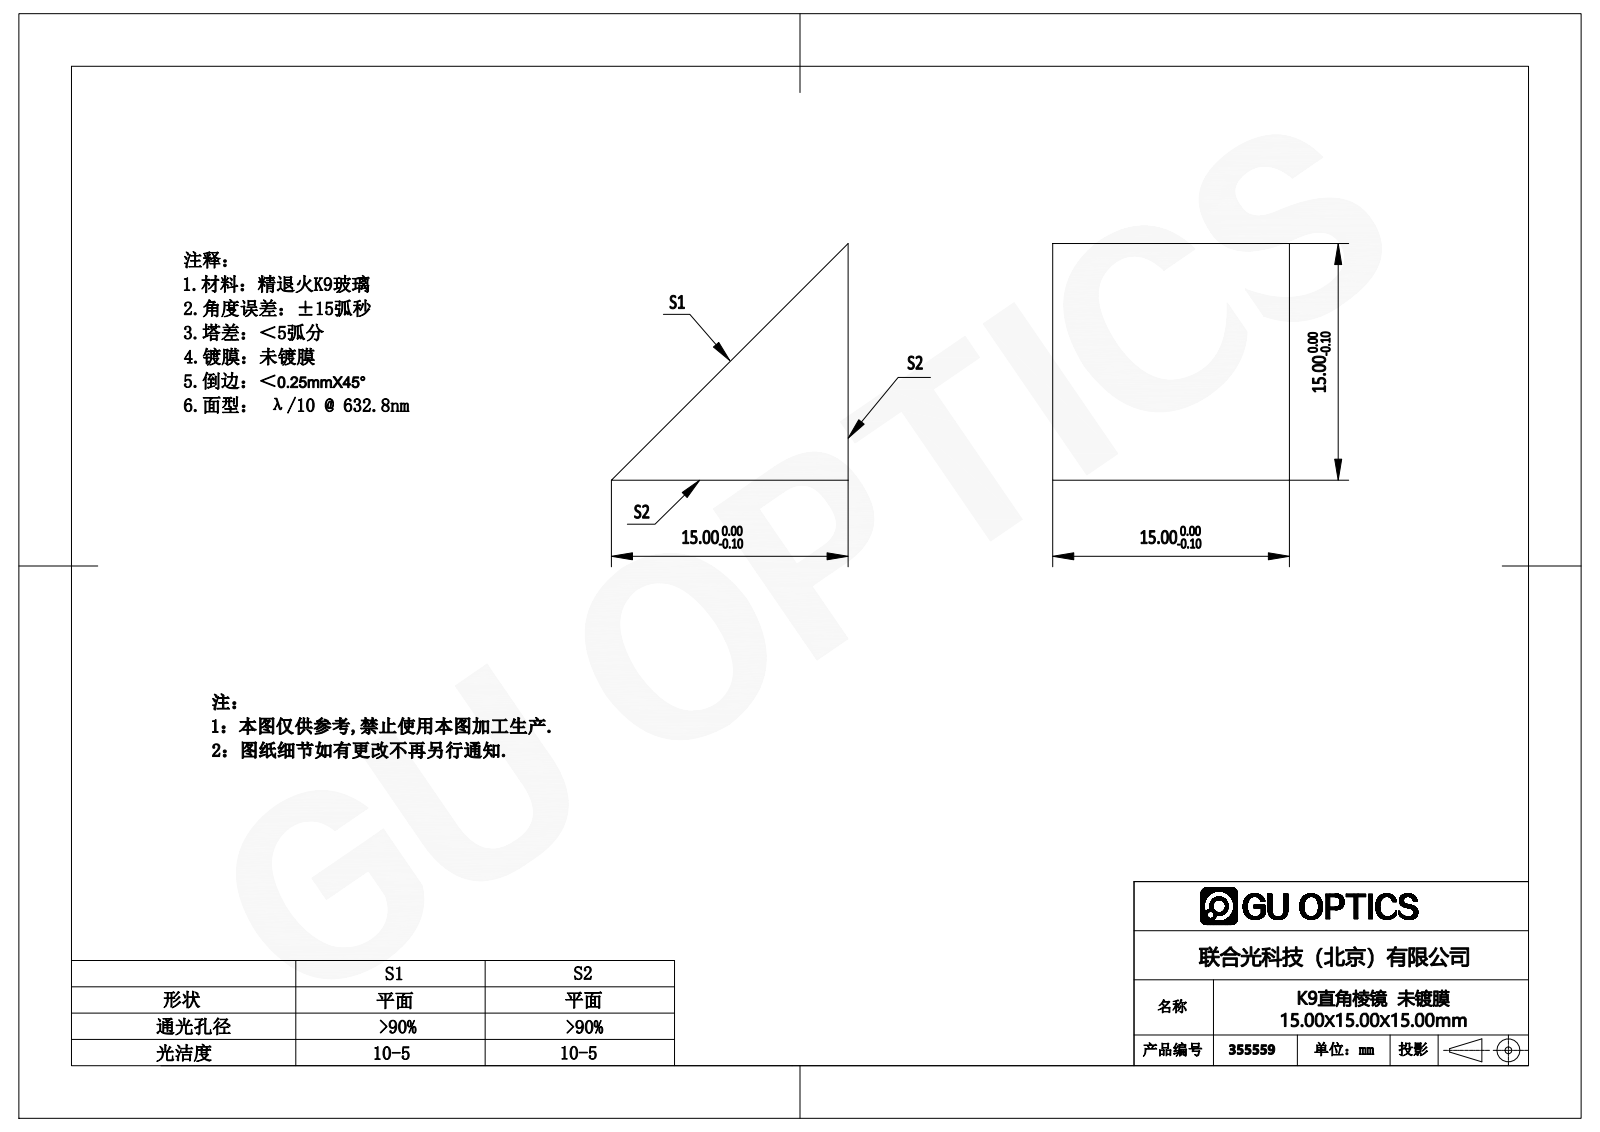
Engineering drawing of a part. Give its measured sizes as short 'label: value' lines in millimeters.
name: 355506
written by: SolidWorks 2016 (CONFIG_CONTROL_DESIGN)
unit: mm
bodies: 1 solid, 5 faces (5 planar, 0 cylindrical, 0 other)
size: 15 × 15 × 15
volume: 1 688 mm³; area: 993 mm²
face distances: 15
